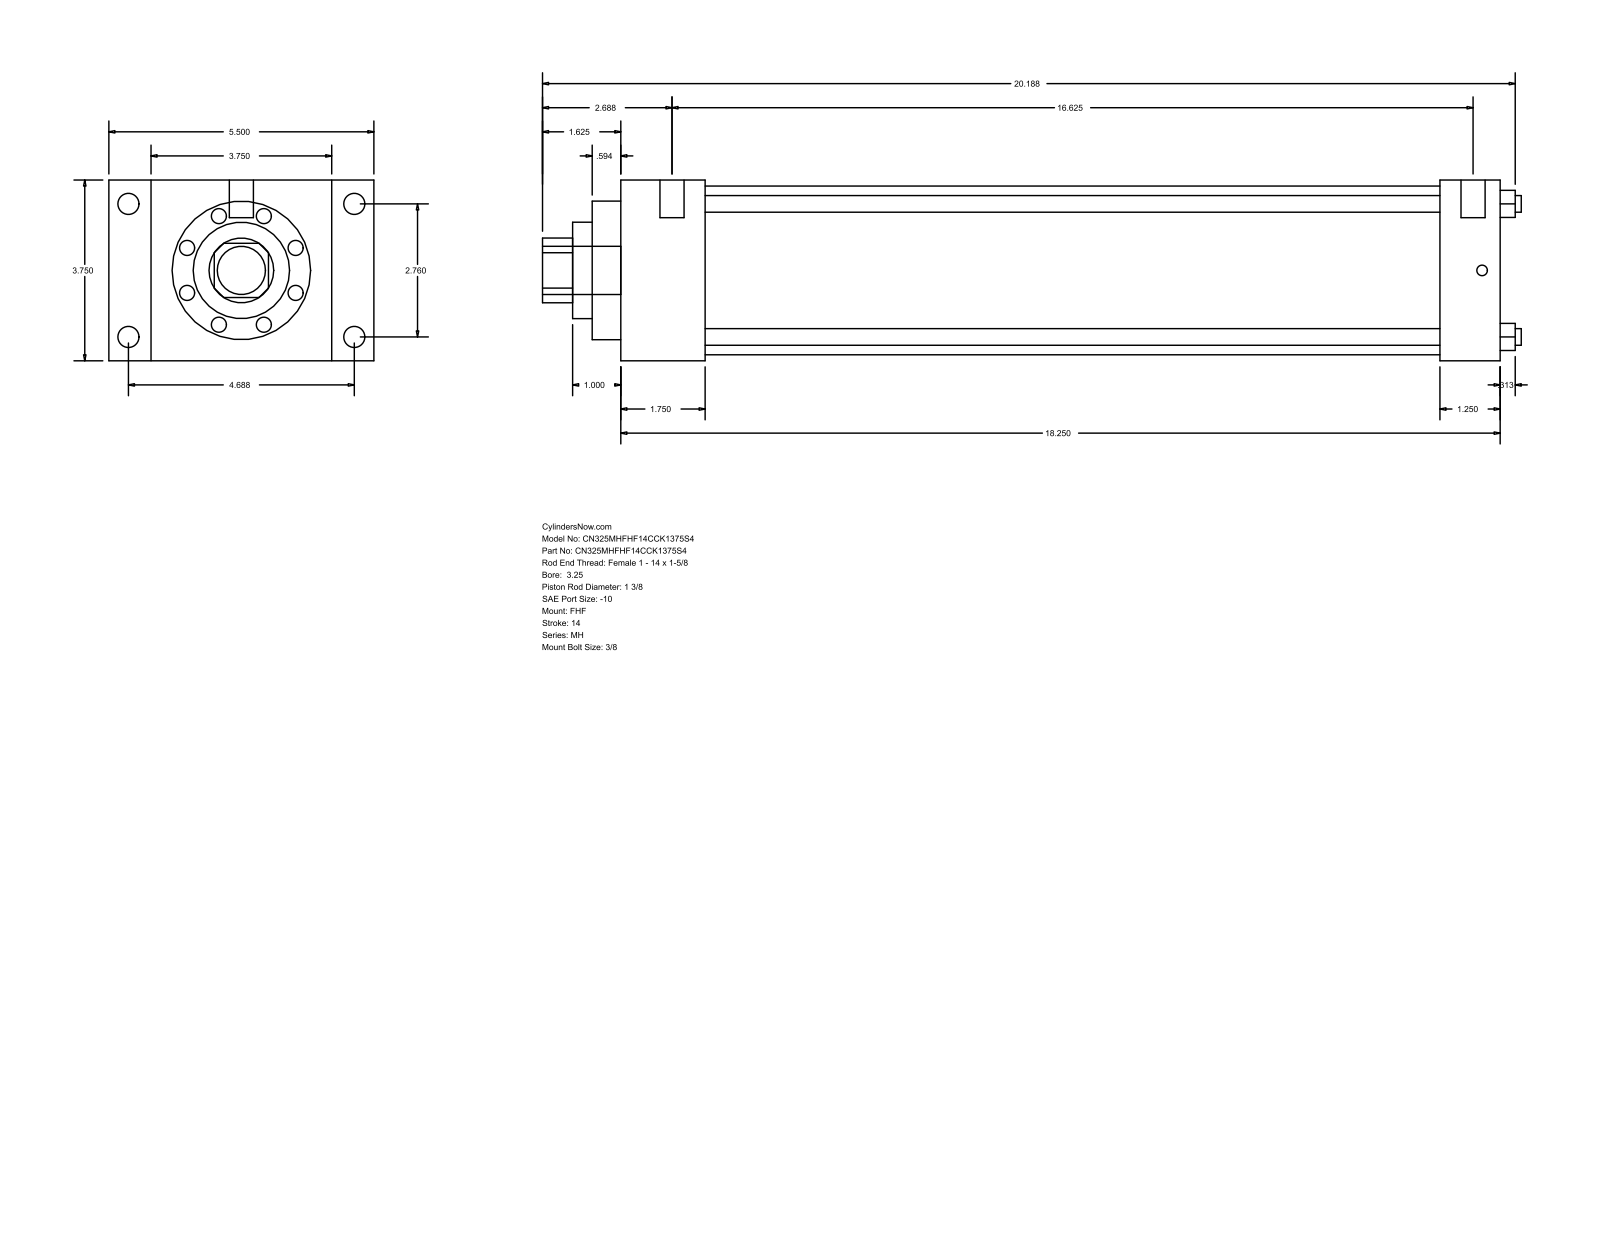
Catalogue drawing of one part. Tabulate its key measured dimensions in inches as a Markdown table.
| quantity | value |
| --- | --- |
| part name | MH_FHF__0325_1.375 |
| STEP written by | GSSL Pune (CONFIG_CONTROL_DESIGN) |
| units | inches |
| bodies | 0 solids, 90 faces (61 planar, 29 cylindrical, 0 other) |
| overall size | 20.313 × 5.5 × 3.75 |
| round holes (diameter × count) | 0.345 × 4, 1.375 × 1, 2 × 1, 2.875 × 1, 3.5 × 1 |
| round bosses / shafts (diameter × count) | 0.438 × 4, 0.219 × 4, 0.5 × 2, 1 × 1 |
| partial cylindrical surfaces (radius × count) | 0.672 × 1 |
| main face-to-face distances | 3.75, 18.25, 1.75, 16.5, 0.875, 4.625, 5.5, 17, 15.25, 1.25 |
| hole center spacings | 1.952, 2.76, 3.903 |
